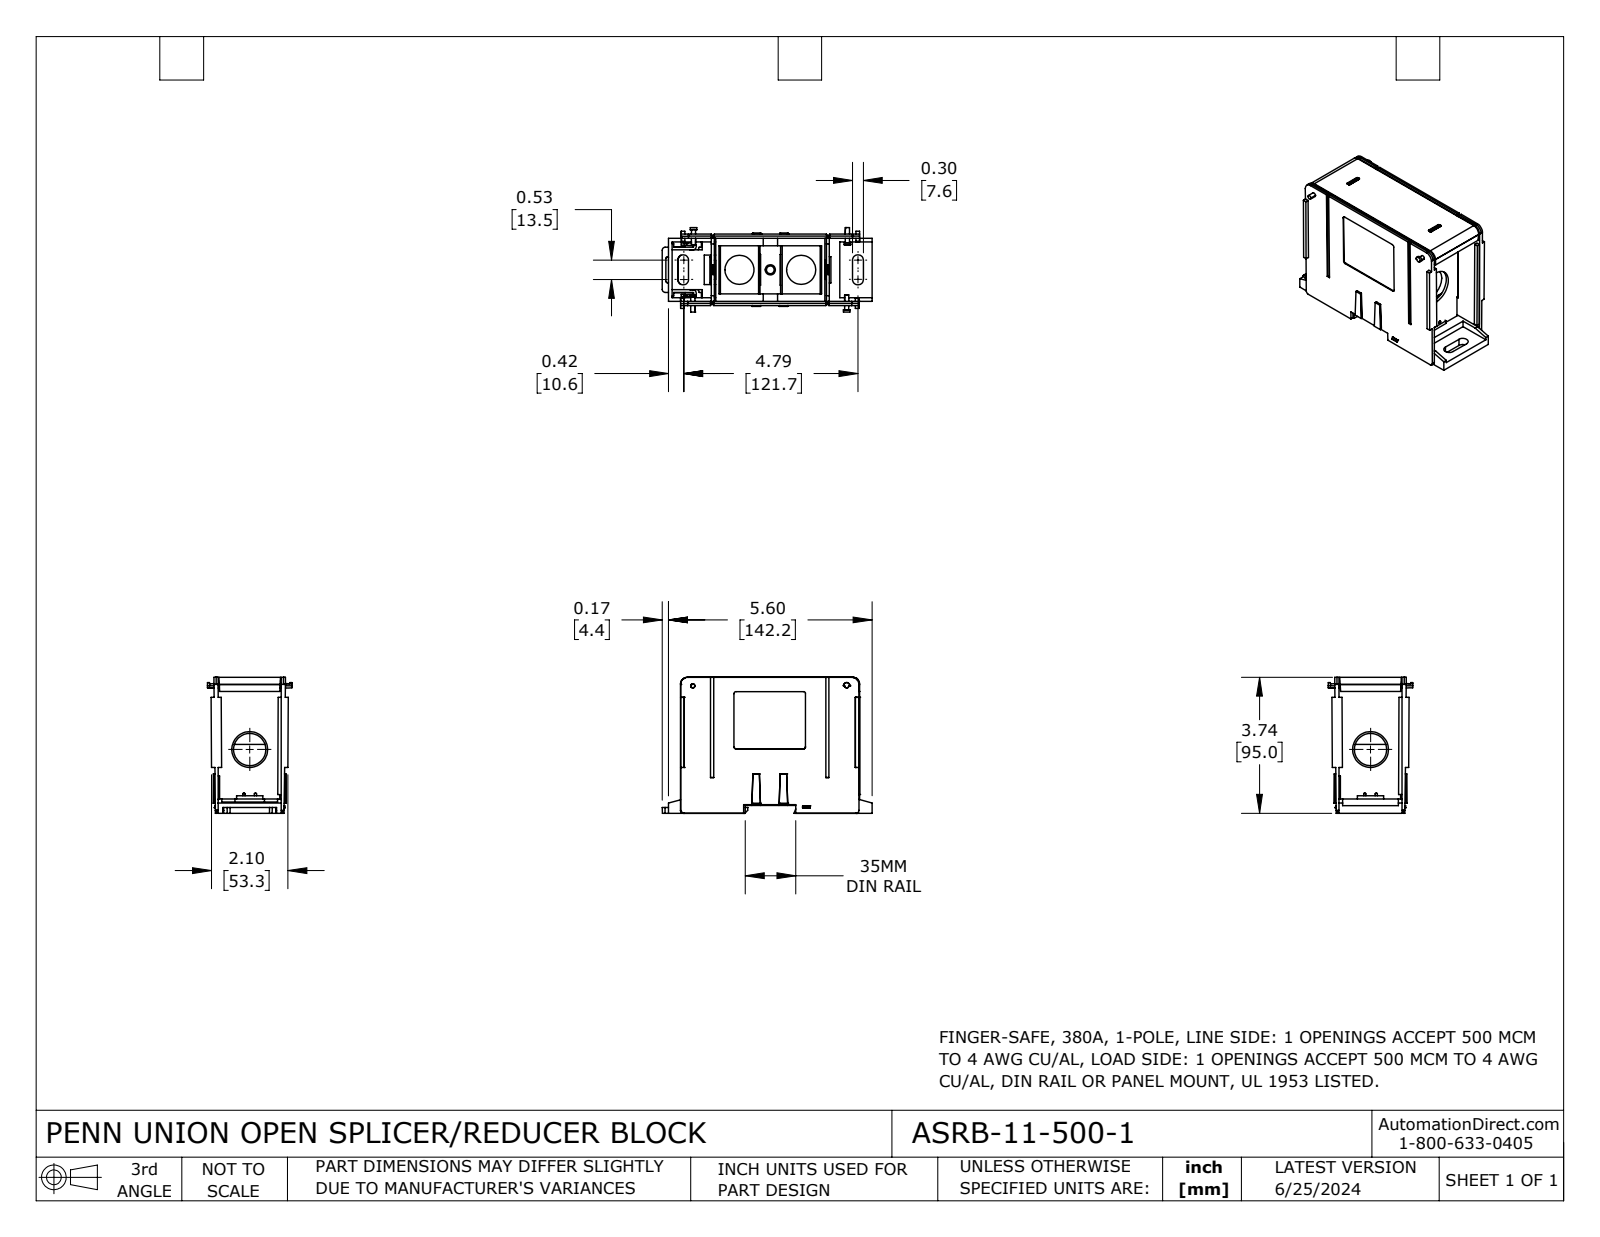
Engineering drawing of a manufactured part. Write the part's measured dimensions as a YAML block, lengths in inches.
part_name: "ASRB-11-500-1"
step_written_by: "SolidWorks 2023 (CONFIG_CONTROL_DESIGN)"
units: inches
bodies: {solids: 10, faces: 756, planar: 541, cylindrical: 144, other: 71}
overall_size: [5.77, 3.741, 2.321]
volume: 14
surface_area: 196.2
round_holes:
  - {diameter: 0.213, count: 1}
  - {diameter: 0.28, count: 1}
  - {diameter: 0.798, count: 1}
  - {diameter: 0.798, count: 1}
  - {diameter: 0.886, count: 1}
  - {diameter: 0.984, count: 1}
partial_cylinders:
  - {radius: 0.039, count: 26}
  - {radius: 0.059, count: 18}
  - {radius: 0.02, count: 16}
  - {radius: 0.079, count: 10}
  - {radius: 0.197, count: 10}
  - {radius: 0.012, count: 6}
  - {radius: 0.089, count: 4}
  - {radius: 0.15, count: 4}
face_to_face_distances: [1.732, 0.079, 3.161, 0.207, 2.539, 2.468, 0.071, 0.02, 1.526, 0.226]
hole_center_spacings: [0.848, 1.697]
